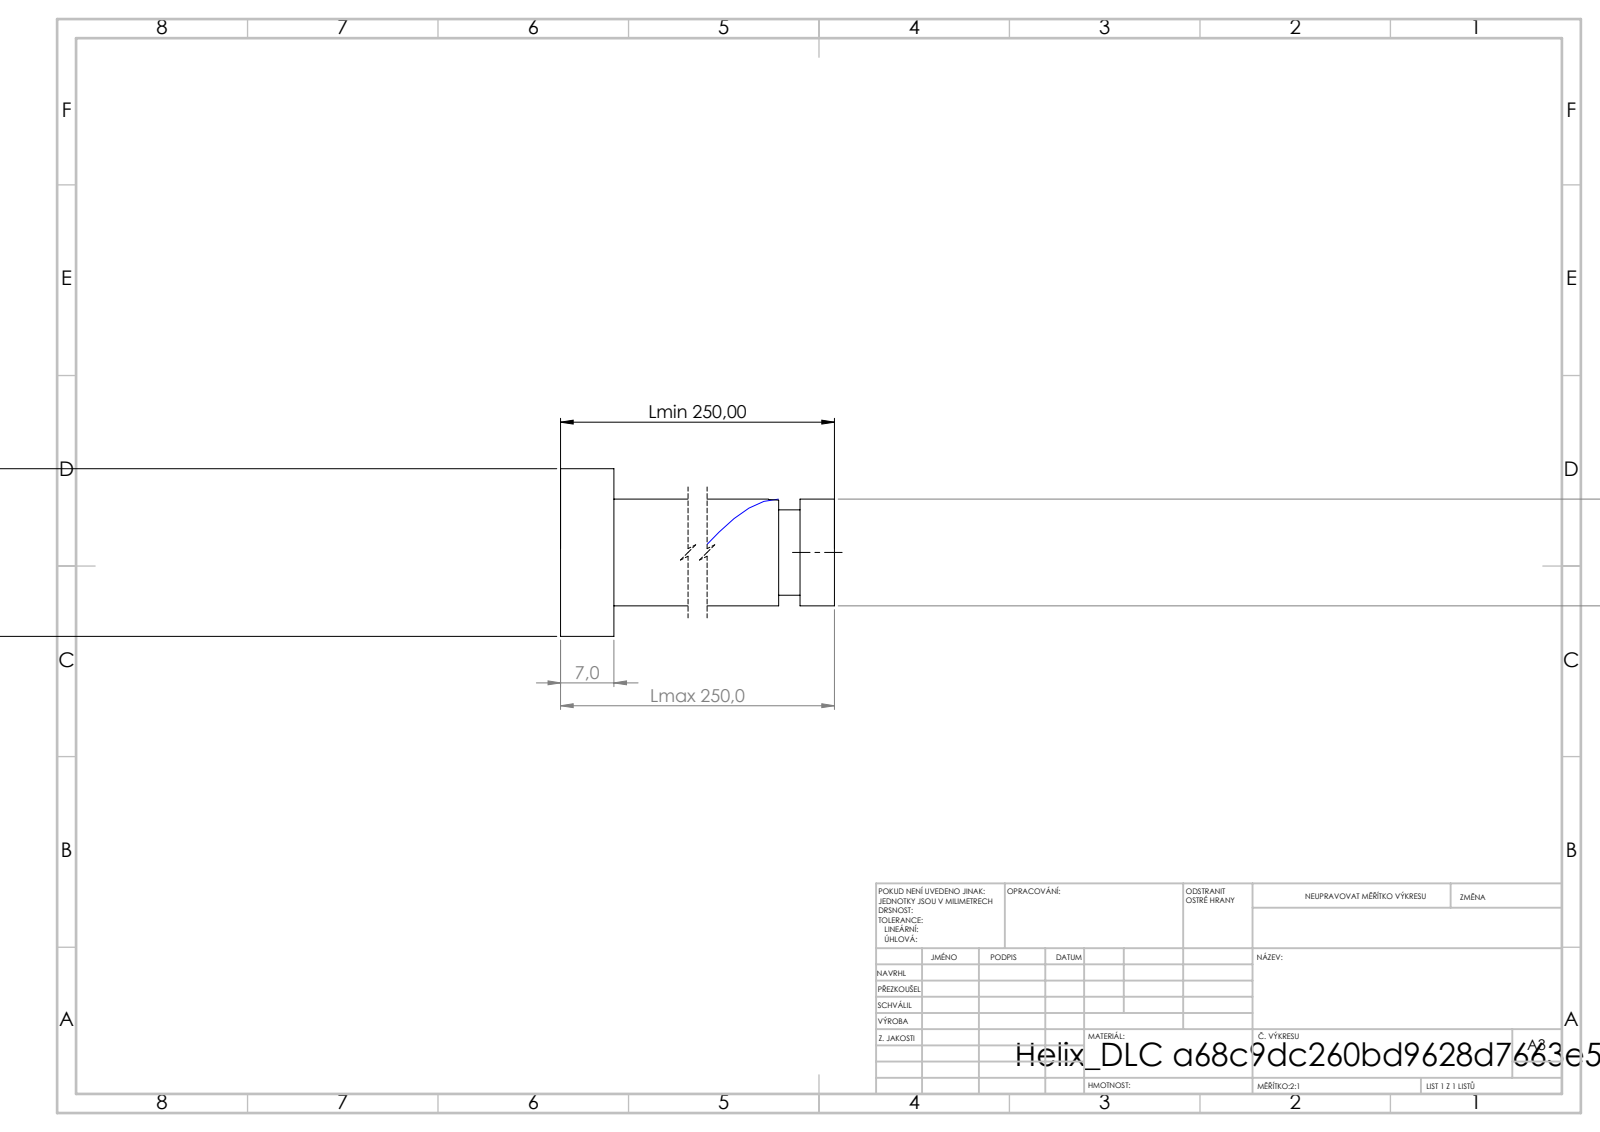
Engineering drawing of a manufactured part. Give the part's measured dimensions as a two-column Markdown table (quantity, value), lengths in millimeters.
| quantity | value |
| --- | --- |
| STEP written by | SolidWorks 2019 (CONFIG_CONTROL_DESIGN) |
| units | millimeters |
| bodies | 1 solid, 21 faces (6 planar, 14 cylindrical, 1 other) |
| overall size | 250 × 22 × 22 |
| volume | 39 544 mm³ |
| surface area | 12 297 mm² |
| round bosses / shafts (diameter × count) | 22 × 1, 14 × 1, 11.2 × 1 |
| main face-to-face distances | 7, 250, 243, 245.48, 238.48, 4.52, 242.68, 235.68, 2.8, 7.32 |
